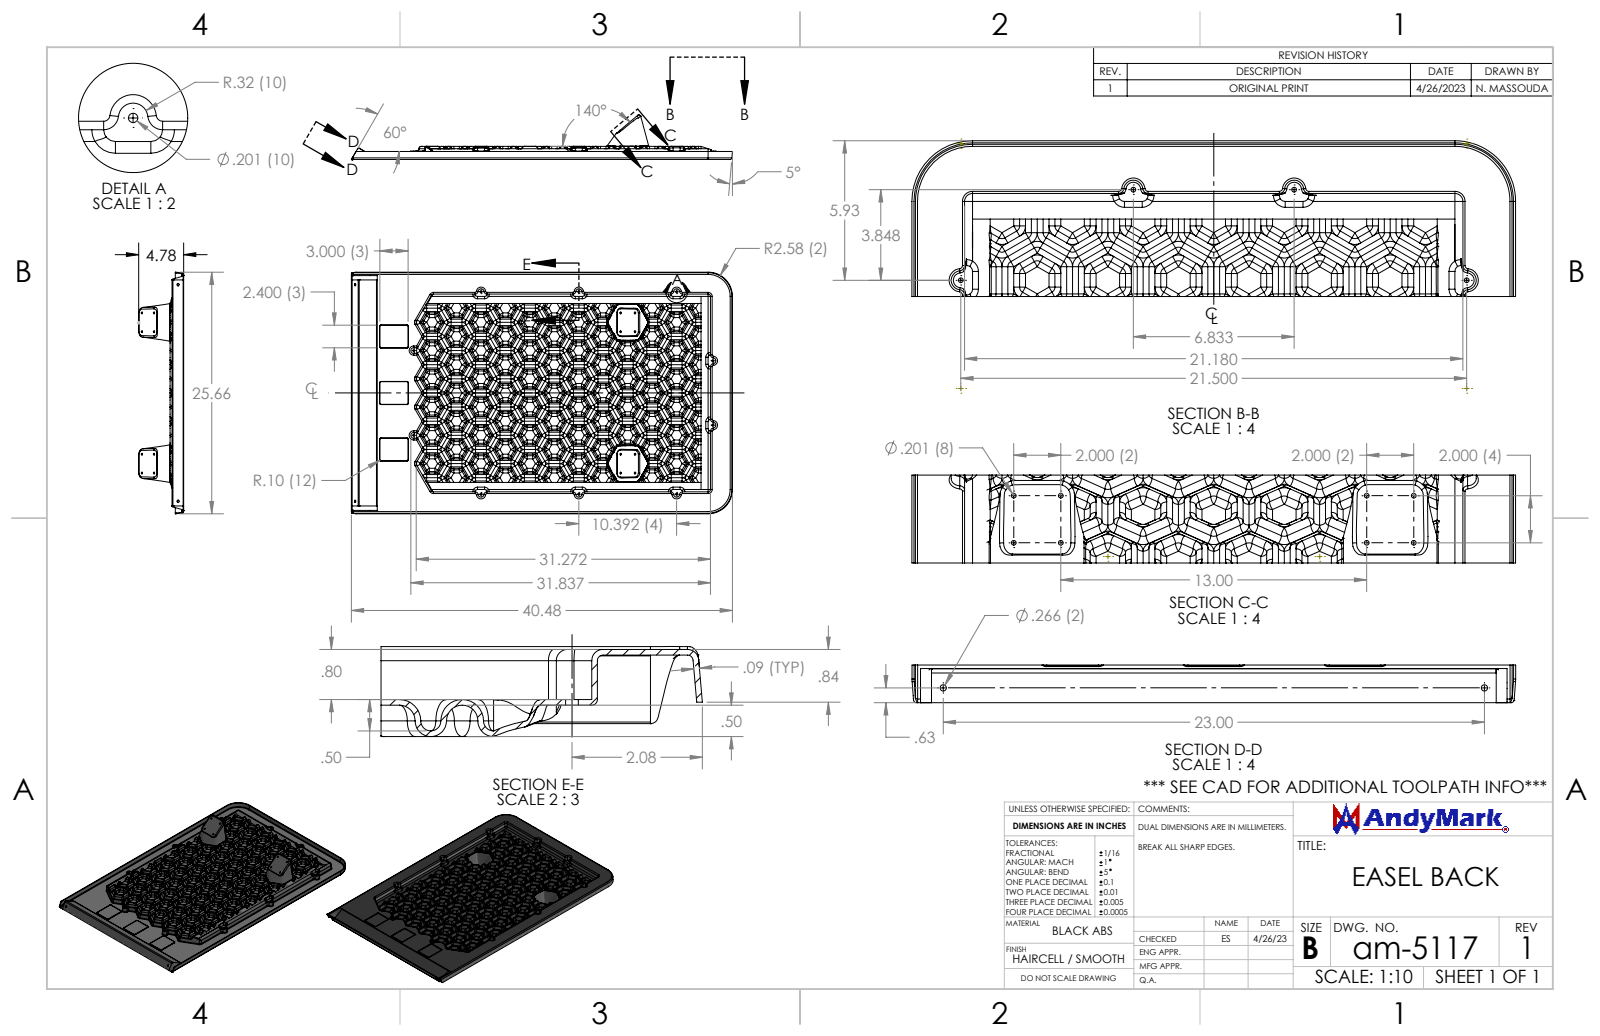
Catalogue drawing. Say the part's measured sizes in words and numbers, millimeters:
The part is named "am-5117 Easel Back". Its 3-D file was written by "SolidWorks 2022 (AUTOMOTIVE_DESIGN)". It is 1 solid with 10084 faces: 1382 planar, 3849 cylindrical and 4853 other. Overall it measures 1028.2 by 651.7 by 121.4 millimeters. Its volume is 2 488 000 cubic millimeters and its surface area 2 002 000 square millimeters. Round holes: 18 of diameter 5.1, 2 of diameter 6.8. Partial cylindrical surfaces (rounded edges, fillets, slot ends): 483 of radius 6.4, 275 of radius 4.1, 273 of radius 8.6, 44 of radius 2.3, 28 of radius 4.6, 26 of radius 8, 24 of radius 0.6, 16 of radius 5.7. The main face-to-face distances are 2.3, 20.3, 22.6, 18, 1.3, 19, 2.3, 535.7, 3.6, 16.7. The hole center spacings are 50.8, 71.8, 381, 384.4, 606.6, 546.1, 210.4, 241.
